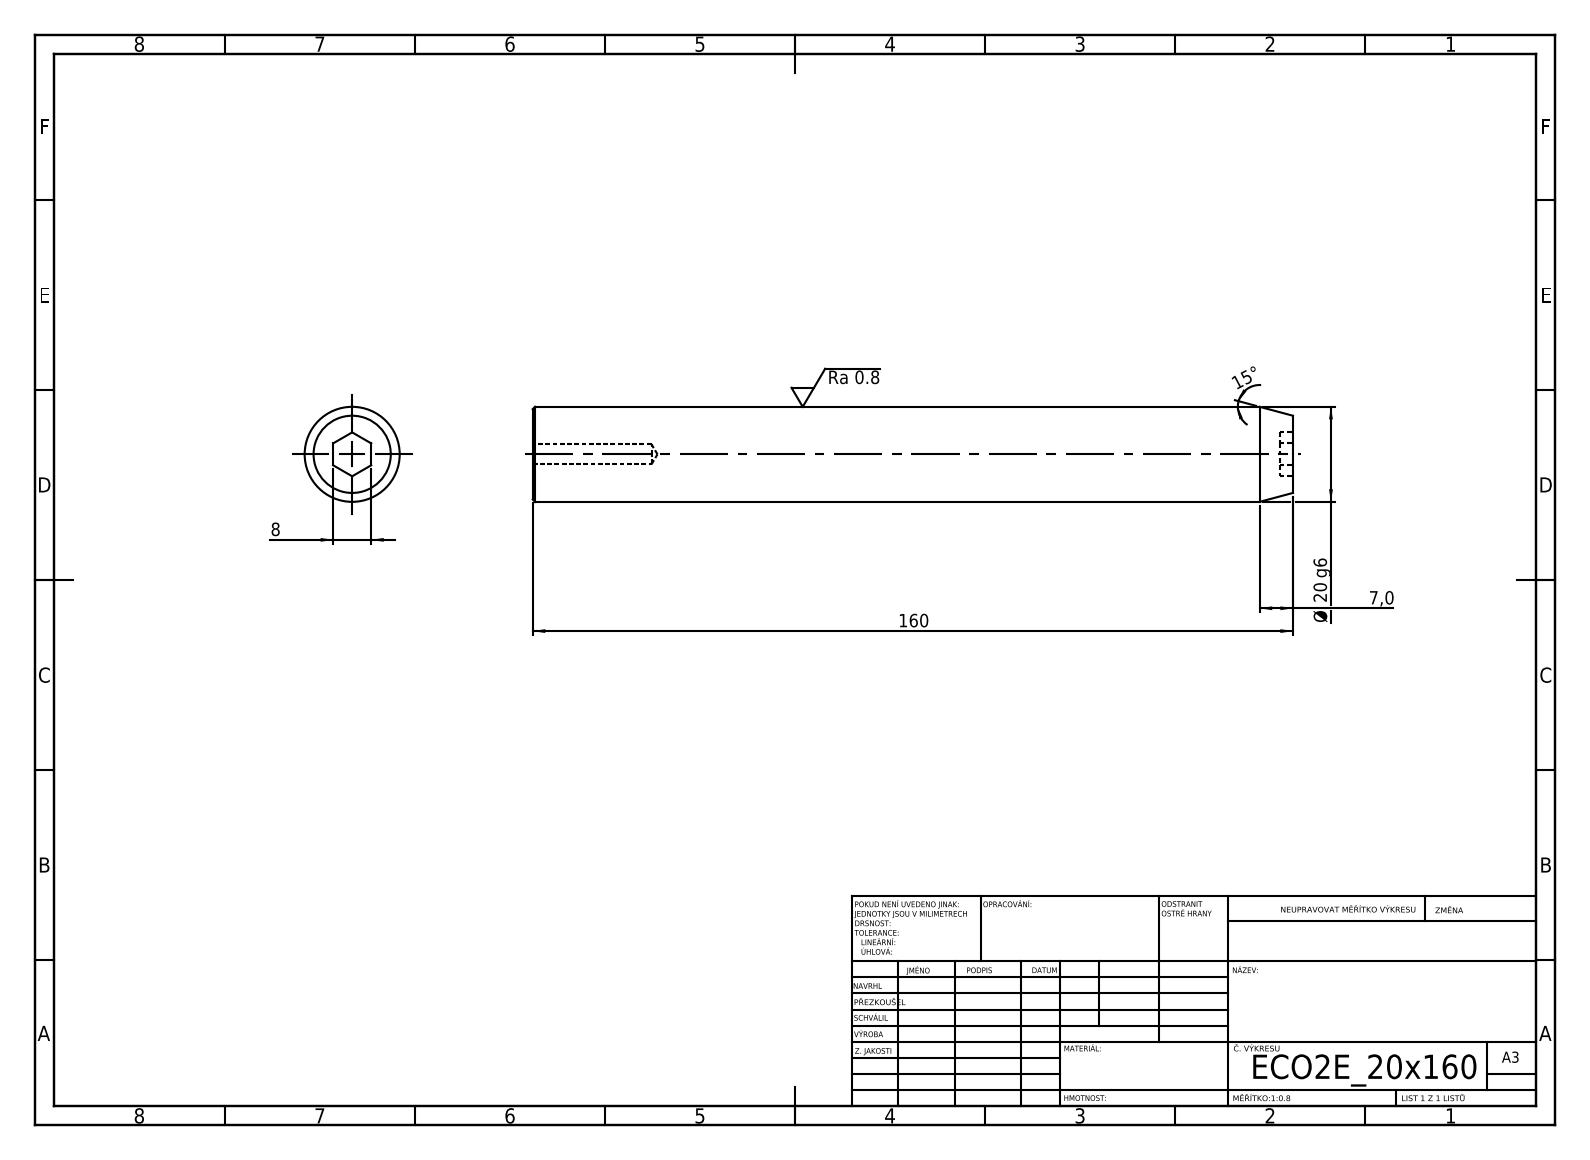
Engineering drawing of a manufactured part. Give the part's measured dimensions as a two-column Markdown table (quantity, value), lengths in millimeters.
| quantity | value |
| --- | --- |
| STEP written by | SolidWorks 2019 (CONFIG_CONTROL_DESIGN) |
| units | millimeters |
| bodies | 1 solid, 19 faces (9 planar, 4 cylindrical, 6 other) |
| overall size | 160 × 20 × 20 |
| volume | 49 364 mm³ |
| surface area | 10 938 mm² |
| round holes (diameter × count) | 4.2 × 1 |
| round bosses / shafts (diameter × count) | 20 × 1 |
| main face-to-face distances | 160, 2.8, 157.2, 8 |
